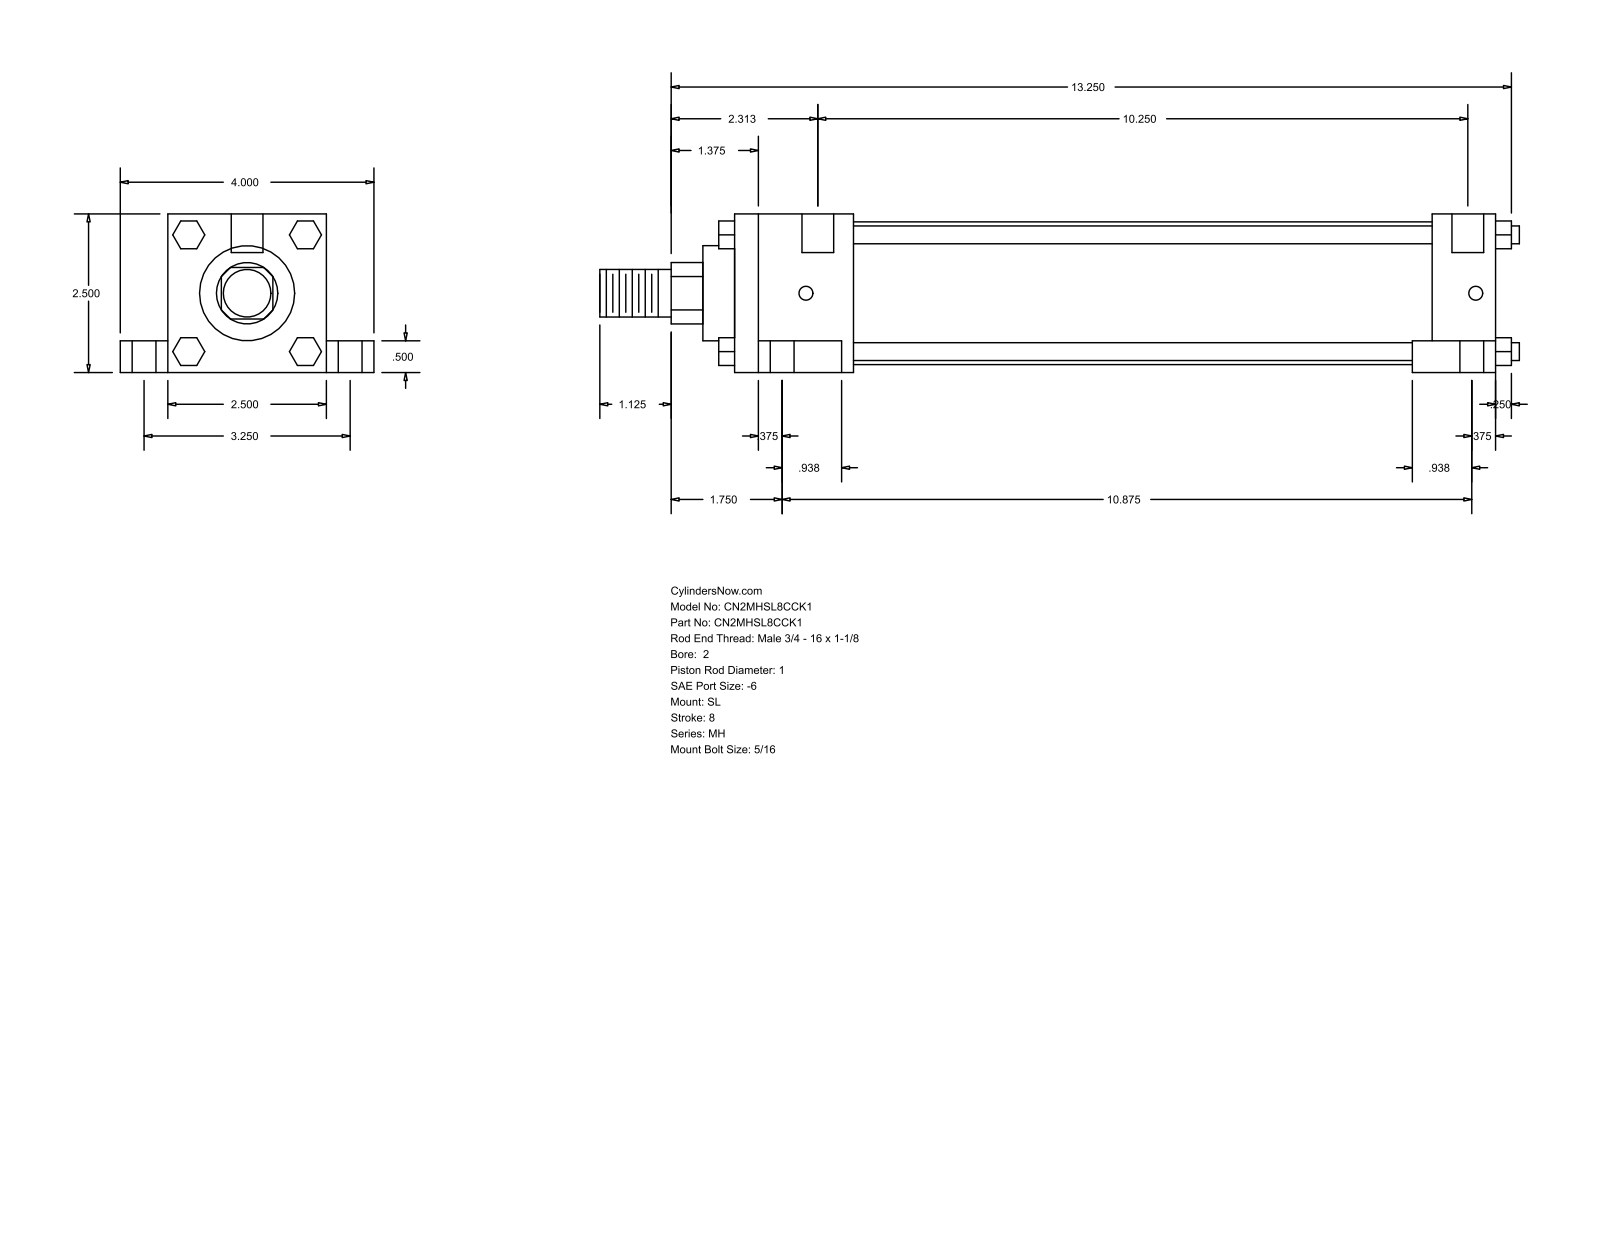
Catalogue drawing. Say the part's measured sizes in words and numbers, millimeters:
The part is named "MH_SL__0200_1". Its 3-D file was written by "GSSL Pune (CONFIG_CONTROL_DESIGN)". It is 0 solids with 148 faces: 112 planar, 36 cylindrical and 0 other. Overall it measures 368.3 by 101.6 by 63.5 millimeters. Round holes: 4 of diameter 5.56, 4 of diameter 9.53, 4 of diameter 15.88, 2 of diameter 12.7. Round bosses or shafts: 4 of diameter 7.14, 1 of diameter 57.15, 1 of diameter 38.1, 1 of diameter 25.4, 1 of diameter 19.05. Partial cylindrical surfaces (rounded edges, fillets, slot ends): 1 of radius 12.29. The main face-to-face distances are 63.5, 304.8, 12.7, 19.05, 50.8, 82.55, 25.4, 279.4, 47.63, 231.77. The hole center spacings are 41.3, 42.36, 43.67, 82.54, 265.17, 268.28, 269.87, 276.23.
